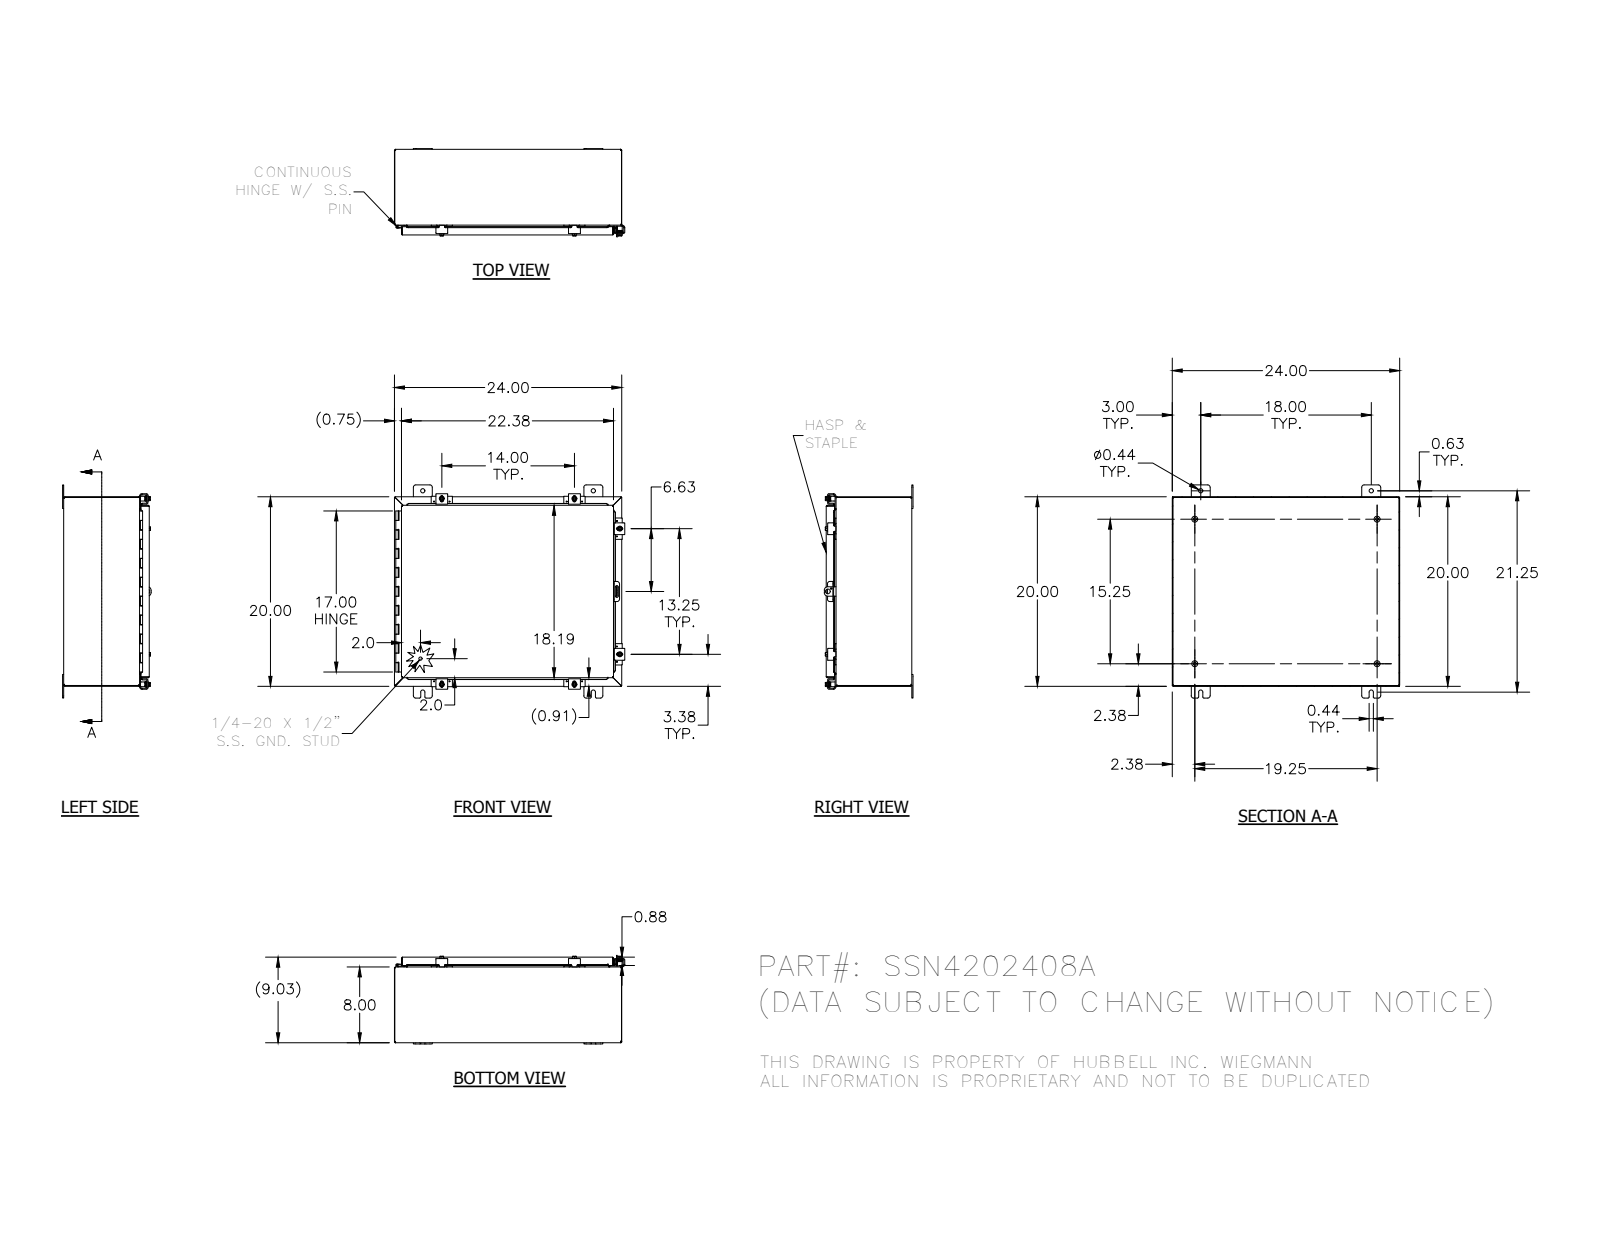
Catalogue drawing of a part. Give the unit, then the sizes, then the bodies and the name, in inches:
Units: inches
Overall size (bounding box): 24.216 × 22.5 × 9.355
Round holes (diameter × count): ⌀0.11 ×12, ⌀0.211 ×6, ⌀0.281 ×6, ⌀0.3 ×6, ⌀0.438 ×4, ⌀0.125 ×1, ⌀0.156 ×1, ⌀0.5 ×1
Round bosses / shafts (diameter × count): ⌀0.25 ×8, ⌀0.52 ×6, ⌀0.5 ×6, ⌀0.35 ×6, ⌀0.625 ×4, ⌀0.33 ×4, ⌀0.337 ×1, ⌀0.12 ×1
Partial cylindrical surfaces — rounded edges, fillets, slot ends (radius × count): R0.03 ×71, R0.125 ×35, R0.25 ×31, R0.031 ×23, R0.105 ×23, R0.062 ×16, R0.141 ×12, R0.07 ×8
Main face-to-face distances: 0.074, 8.959, 8.885, 9.033, 19.926, 23.926, 7.926, 1.033, 20, 19.852
Hole centre spacings: 0.876, 19.306, 14, 1.625, 13.191, 14.816, 18.961, 19.03
Volume: 153 in³ · Surface area: 4 004 in²
Bodies: 47 solids, 1796 faces (697 planar, 774 cylindrical, 325 other)
Part name (STEP PRODUCT): 30818; 32874-20T; 38859; 38846 (+8 more)
STEP written by: SolidWorks 2014 (AUTOMOTIVE_DESIGN)
